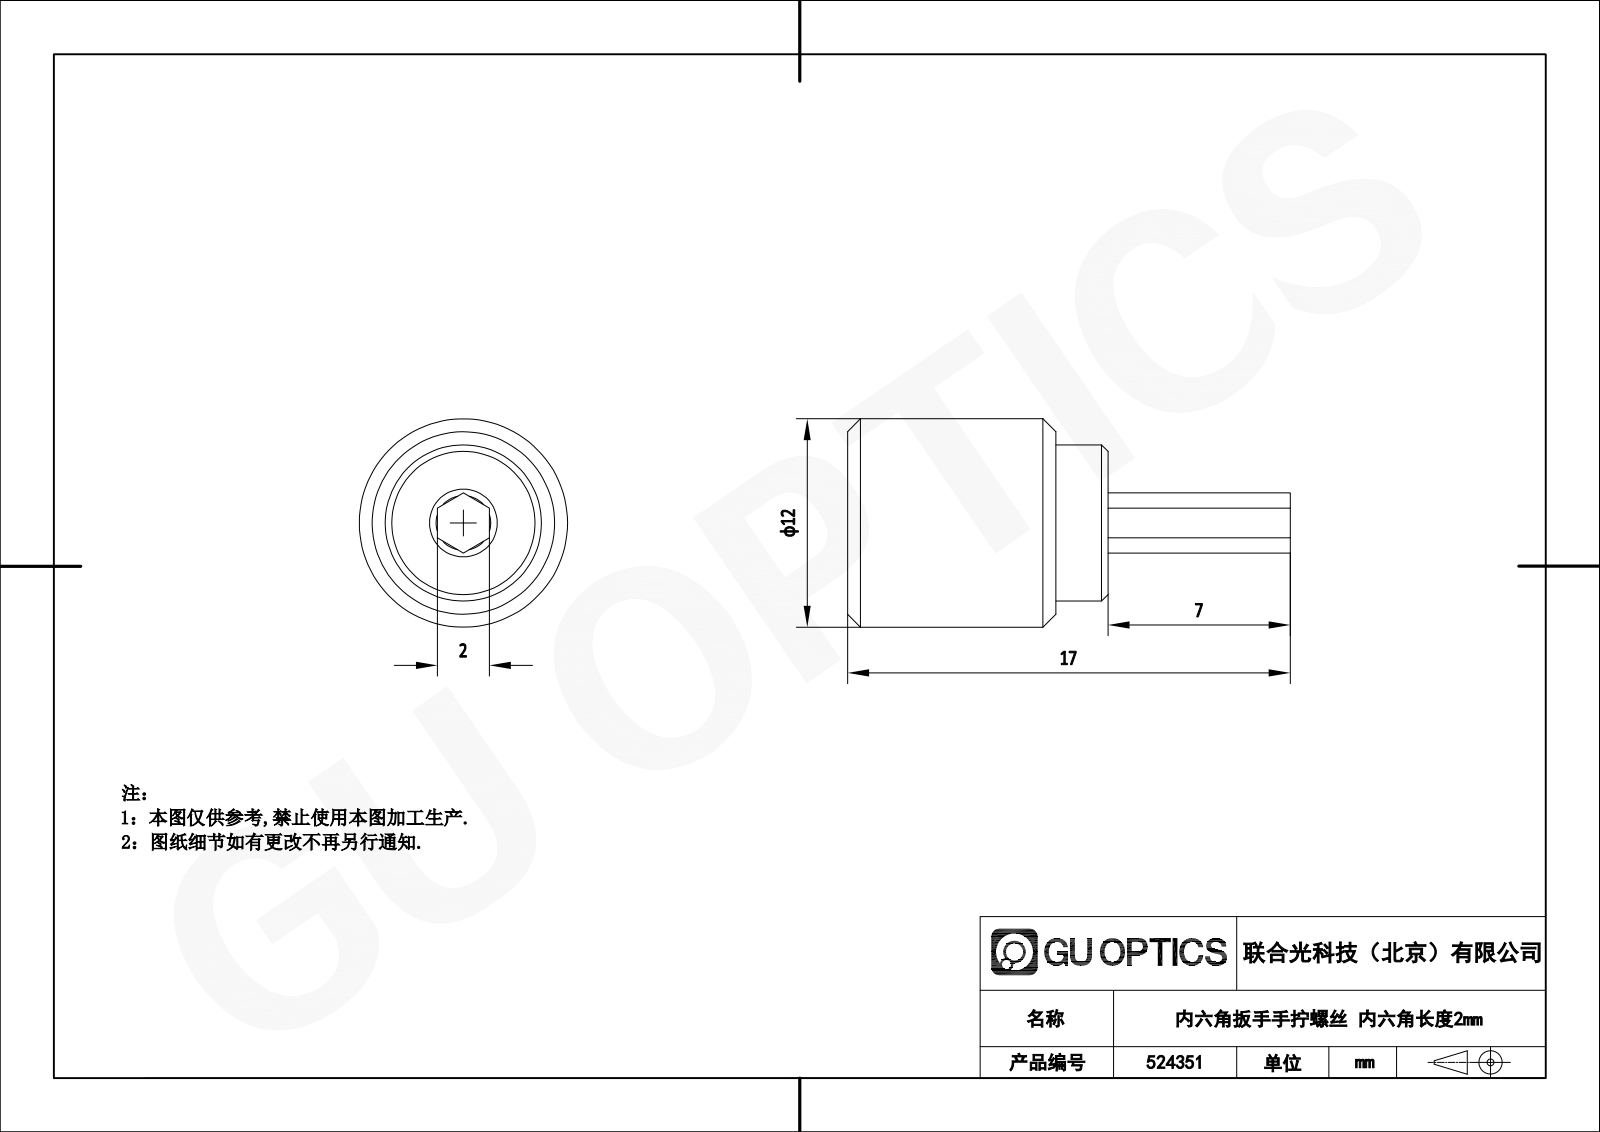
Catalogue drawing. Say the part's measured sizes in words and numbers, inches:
The part is named "1.8.4.2.2_直杆式2x2mm六角扳手，长度11mm，零部件". Its 3-D file was written by "SolidWorks 2021 (CONFIG_CONTROL_DESIGN)". It is 2 solids with 26 faces: 12 planar, 6 cylindrical and 8 other. Overall it measures 0.669 by 0.472 by 0.472 inches. Its volume is 0.066 cubic inches and its surface area 1.05 square inches. Round holes: 1 of diameter 0.083. Round bosses or shafts: 1 of diameter 0.472, 1 of diameter 0.394. The main face-to-face distances are 0.394, 0.083, 0.079, 0.315, 0.236, 0.157, 0.669, 0.433, 0.354, 0.276.
